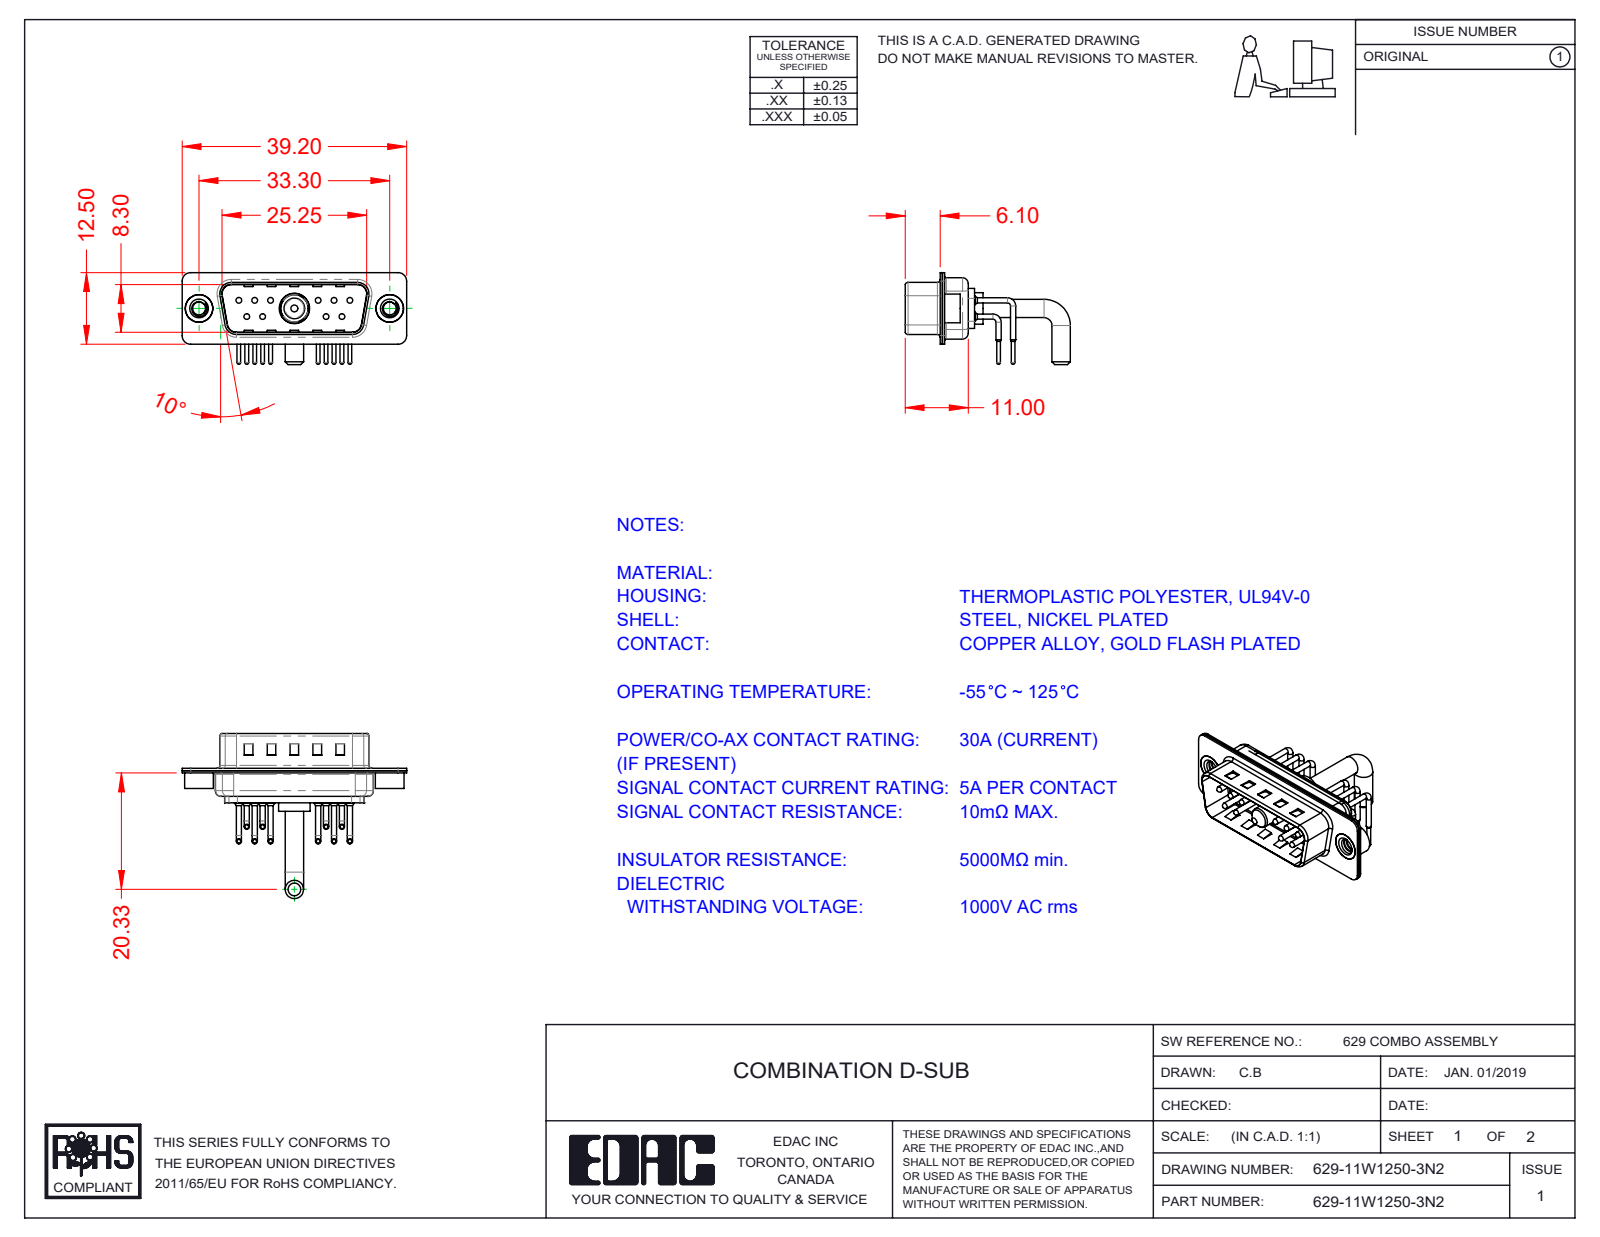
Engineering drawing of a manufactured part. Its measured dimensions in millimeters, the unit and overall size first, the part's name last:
Units: millimetres
Overall size (bounding box): 39.2 × 28.83 × 16.05
Round holes (diameter × count): ⌀0.75 ×10, ⌀1.6 ×10, ⌀2 ×10, ⌀2.26 ×2, ⌀4 ×2, ⌀4.8 ×2, ⌀4.85 ×1, ⌀5.3 ×1
Round bosses / shafts (diameter × count): ⌀0.9 ×20, ⌀1.5 ×10, ⌀1 ×10, ⌀0.65 ×10, ⌀5 ×2, ⌀4.9 ×2, ⌀3.2 ×2, ⌀5.5 ×1
Partial cylindrical surfaces — rounded edges, fillets, slot ends (radius × count): R1.5 ×16, R2 ×12, R1.01 ×10, R0.5 ×8, R1.6 ×8, R1 ×7, R0.25 ×4, R0.6 ×4
Main face-to-face distances: 0.4, 0.8, 9.5, 9.1, 8.7, 9.9, 0.75, 5.6, 1.2, 0.35
Hole centre spacings: 3.16, 2.77, 13.85, 11.08, 16.62, 5.03, 5.04, 5.54
Volume: 2 149 mm³ · Surface area: 5 324 mm²
Bodies: 17 solids, 1496 faces (798 planar, 518 cylindrical, 180 other)
Part name (STEP PRODUCT): 629Combo Shell Front_15 Contacts; 629Combo Housing_11W1; 629Combo Threaded Rivet_2; 629-11W1250-3N2 (+4 more)
STEP written by: SolidWorks 2020 (CONFIG_CONTROL_DESIGN)
